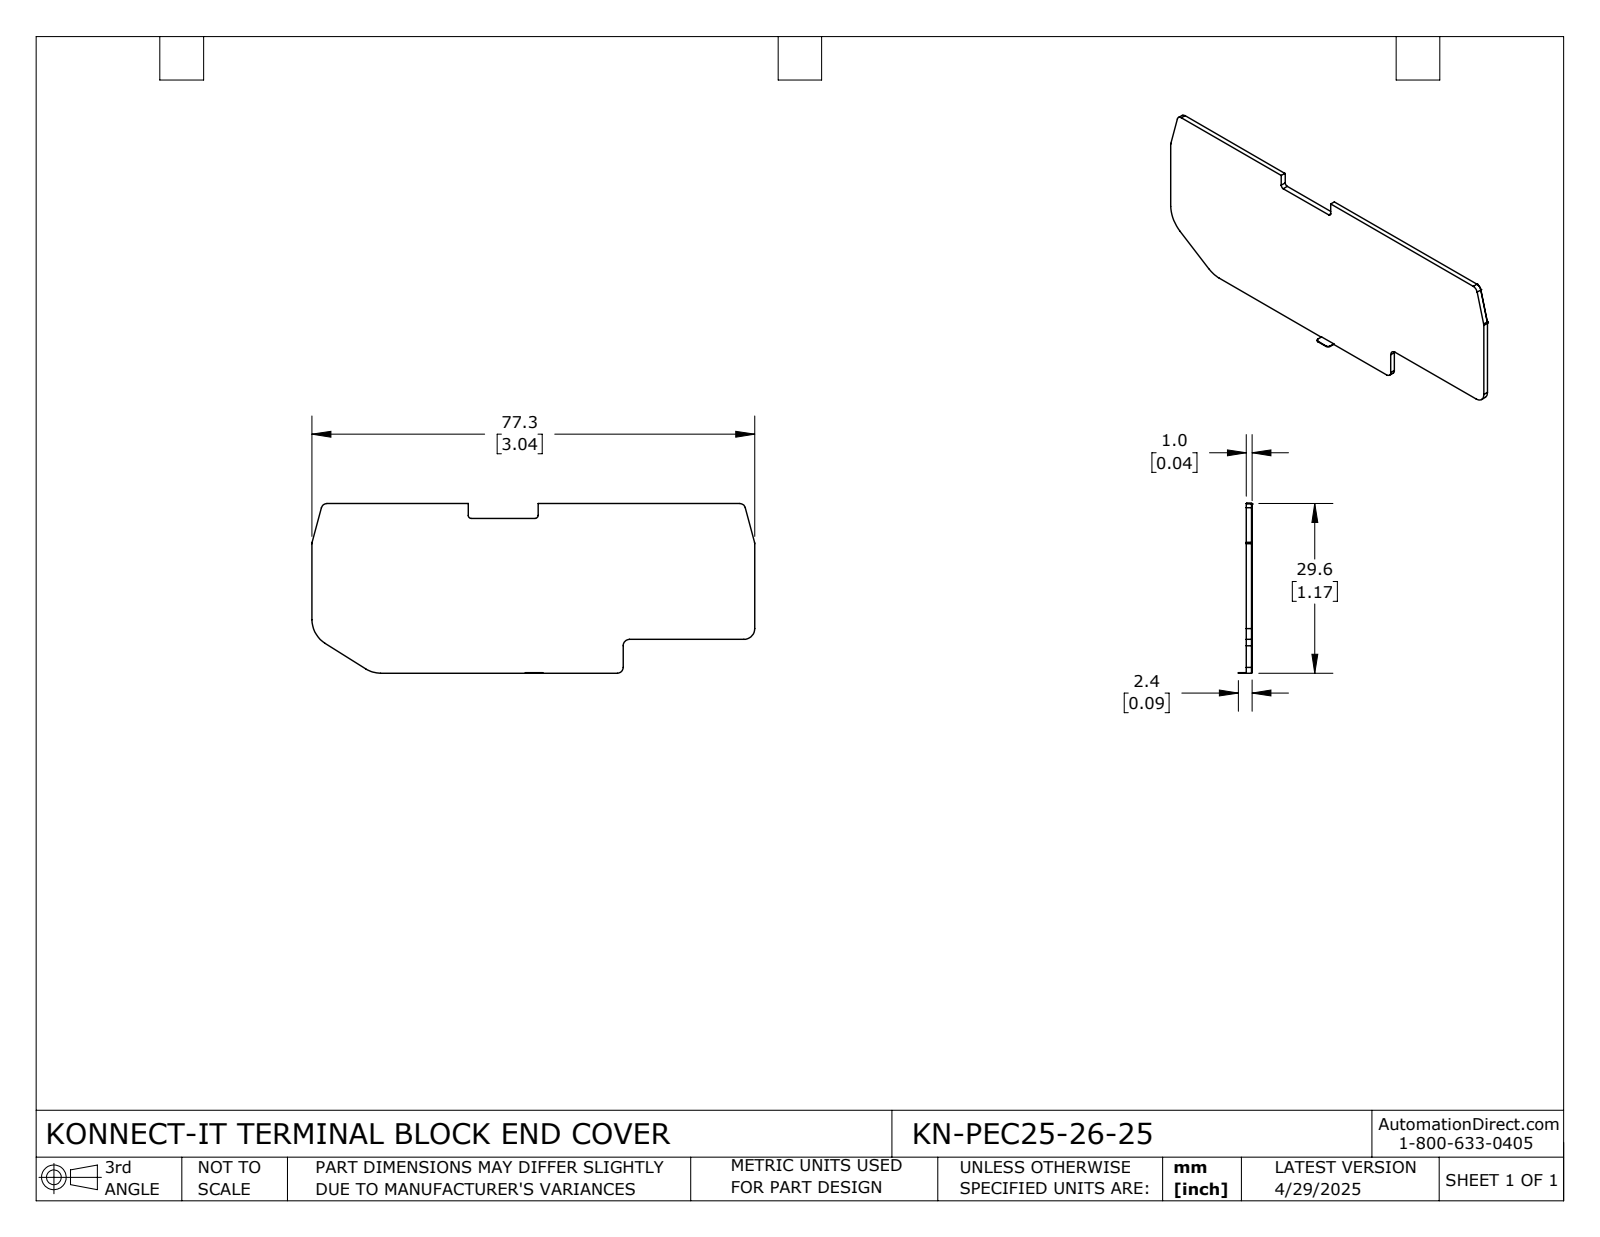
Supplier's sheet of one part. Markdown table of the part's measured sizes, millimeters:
| quantity | value |
| --- | --- |
| part name | KN-PEC25-26-25 |
| STEP written by | SolidWorks 2024 (CONFIG_CONTROL_DESIGN) |
| units | millimeters |
| bodies | 1 solid, 52 faces (30 planar, 22 cylindrical, 0 other) |
| overall size | 77.31 × 29.61 × 2.4 |
| volume | 2 071 mm³ |
| surface area | 4 361 mm² |
| partial cylindrical surfaces (radius × count) | 0.9 × 5, 1 × 5, 0.5 × 4, 4.8 × 2, 4.9 × 2, 1.1 × 1, 1.2 × 1, 1.8 × 1 |
| main face-to-face distances | 1, 29.61, 5.9, 0.9, 23.71, 29.51, 77.31, 27.02, 21.12, 2.59 |
